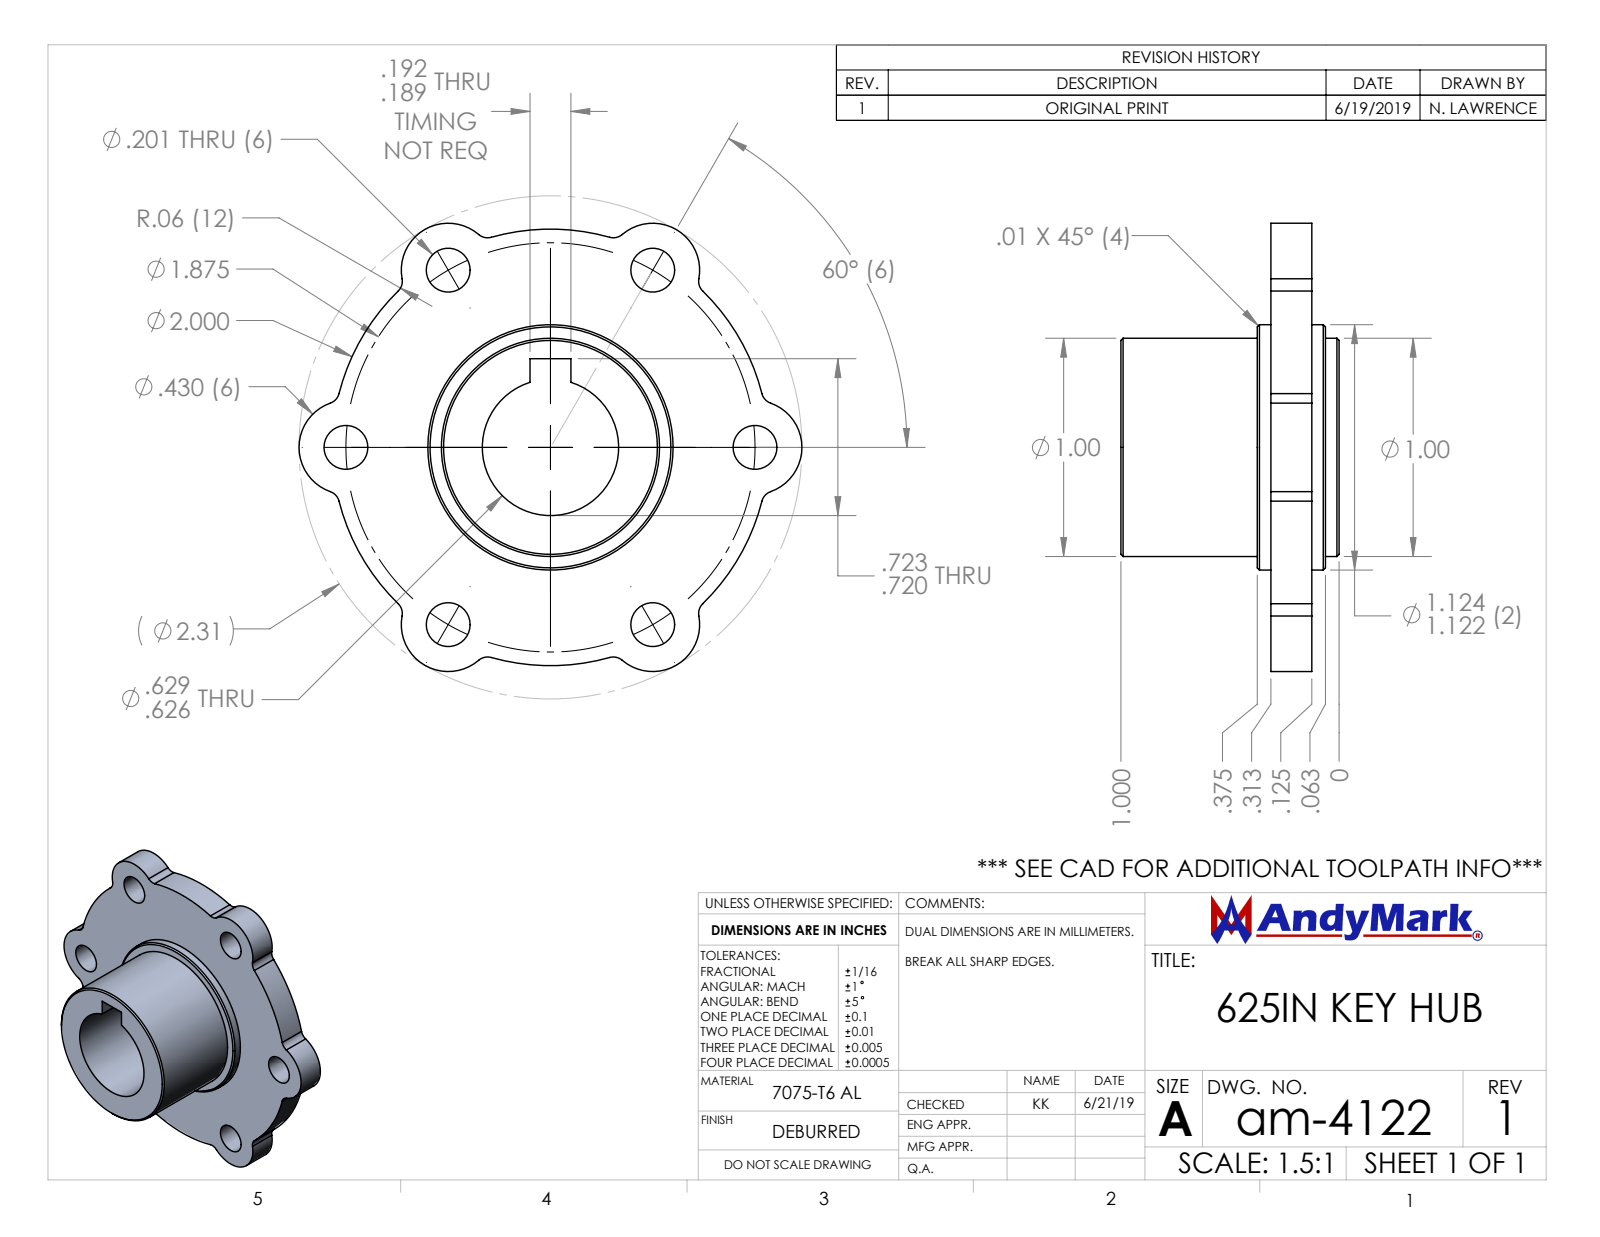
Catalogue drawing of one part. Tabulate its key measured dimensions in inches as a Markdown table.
| quantity | value |
| --- | --- |
| part name | am-4122 625 Key Hub |
| STEP written by | SolidWorks 2019 (AUTOMOTIVE_DESIGN) |
| units | inches |
| bodies | 1 solid, 48 faces (9 planar, 35 cylindrical, 4 other) |
| overall size | 2.305 × 2.054 × 1 |
| volume | 0.947 in³ |
| surface area | 12.61 in² |
| round holes (diameter × count) | 0.201 × 6, 0.625 × 1 |
| round bosses / shafts (diameter × count) | 1.124 × 1, 1 × 1 |
| partial cylindrical surfaces (radius × count) | 0.062 × 9, 0.215 × 6, 0.063 × 3, 1 × 1 |
| main face-to-face distances | 0.187, 0.313, 0.063, 0.125, 1, 0.875, 0.687, 0.25, 0.937, 0.375 |
| hole center spacings | 0.937, 0.938, 1.624, 1.875, 1.624 |
